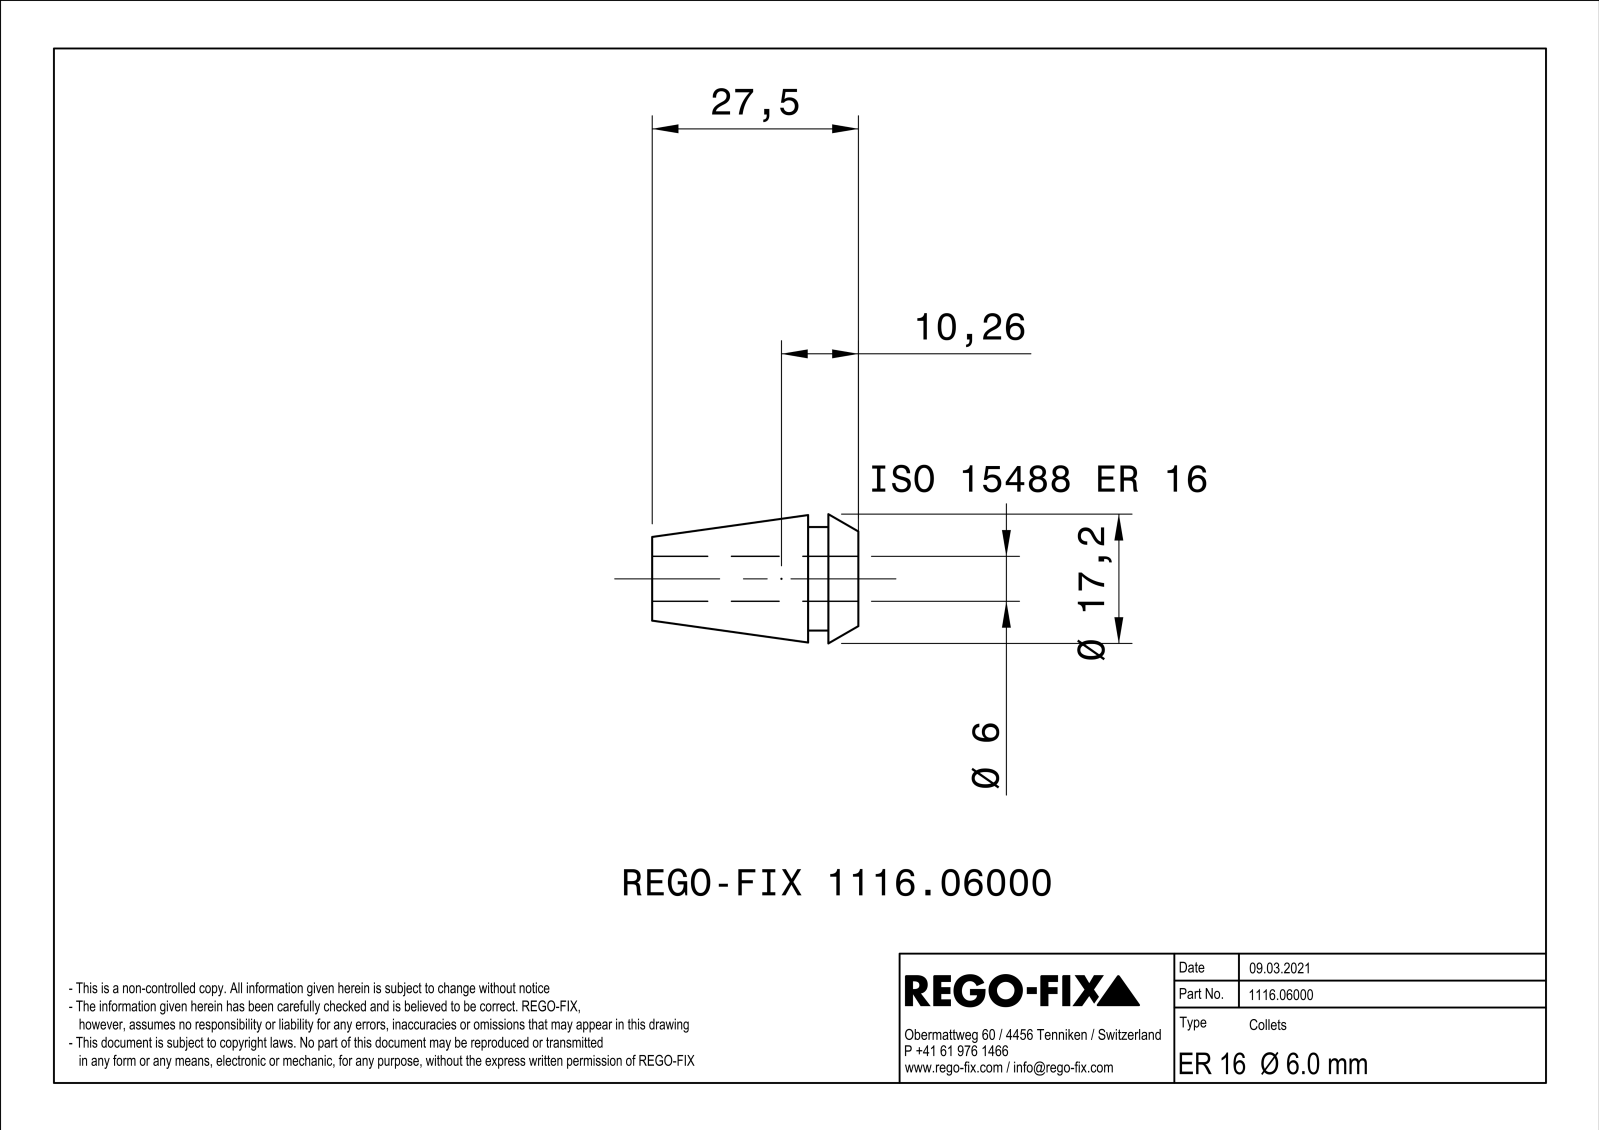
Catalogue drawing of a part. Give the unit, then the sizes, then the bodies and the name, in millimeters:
Units: millimetres
Overall size (bounding box): 27.5 × 17.24 × 17.24
Round holes (diameter × count): ⌀6 ×1
Round bosses / shafts (diameter × count): ⌀13.8 ×1
Partial cylindrical surfaces — rounded edges, fillets, slot ends (radius × count): R0.3 ×8
Main face-to-face distances: 0.6, 4, 6.7, 2.7, 27.5, 23.5, 20.8
Volume: 2 662 mm³ · Surface area: 4 787 mm²
Bodies: 1 solid, 153 faces (72 planar, 25 cylindrical, 56 other)
Part name (STEP PRODUCT): NOCUT
STEP written by: SIEMENS PLM Software Solid Edge ST10 (AUTOMOTIVE_DESIGN)
